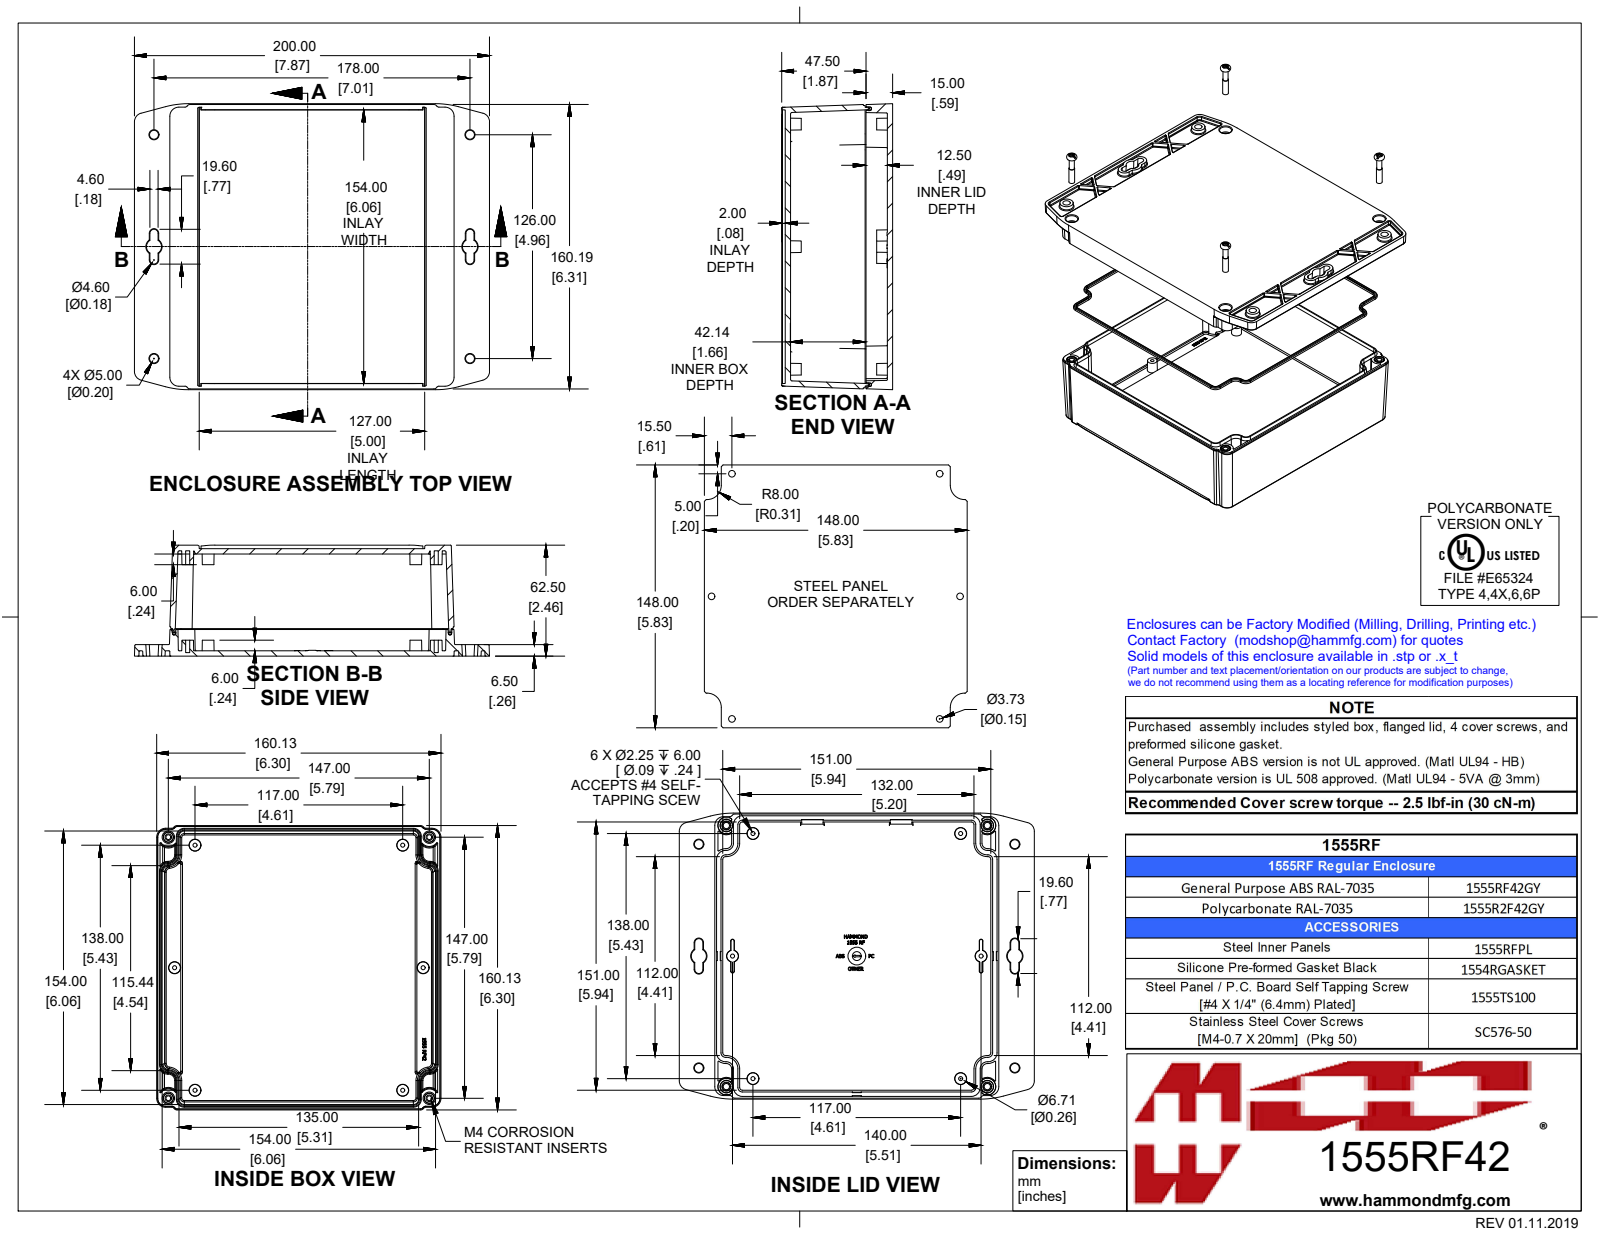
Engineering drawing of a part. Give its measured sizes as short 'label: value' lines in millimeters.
name: 1555R2F42GY
written by: SolidWorks 2019 (CONFIG_CONTROL_DESIGN)
unit: mm
bodies: 11 solids, 2452 faces (811 planar, 493 cylindrical, 1148 other)
size: 200 × 161 × 62.5
volume: 314 000 mm³; area: 213 800 mm²
holes: 6× ⌀2.3, 4× ⌀3.3, 4× ⌀7
bosses: 4× ⌀6.4, 4× ⌀5.5, 4× ⌀5.3, 4× ⌀3.9, 4× ⌀3.4, 1× ⌀10, 1× ⌀5
rounds: 166× R0.5, 13× R0.8, 6× R0.3, 4× R3, 4× R5, 4× R5.1, 4× R50, 2× R1
face distances: 3, 57.5, 3.1, 60.5, 54.5, 3, 3.5, 6.5, 2, 51
hole spacings: 15.7, 70, 73.6, 132.1, 143.3, 145.8, 147, 161.2
